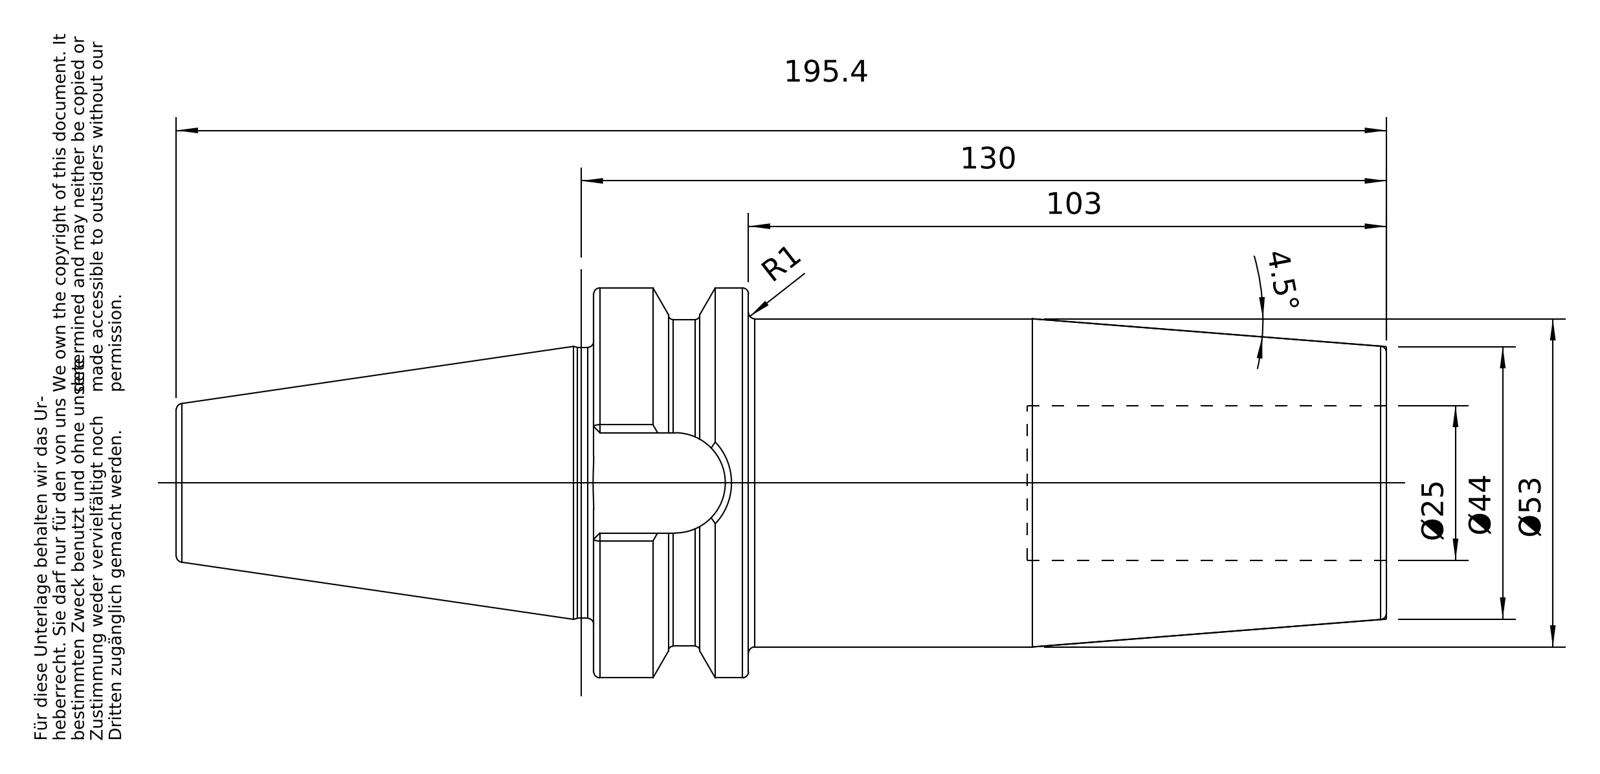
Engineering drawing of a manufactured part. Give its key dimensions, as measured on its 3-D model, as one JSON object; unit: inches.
{"part_name": "40-644-25", "step_written_by": "PRO/ENGINEER BY PARAMETRIC TECHNOLOGY CORPORATION, 2010430 (CONFIG_CONTROL_DESIGN)", "units": "inches", "bodies": {"solids": 1, "faces": 96, "planar": 26, "cylindrical": 22, "other": 48}, "overall_size": [7.693, 2.48, 2.48], "volume_in3": 18.59, "surface_area_in2": 65.02, "round_holes": [[0.545, 1], [0.67, 1], [0.689, 1], [0.984, 1]], "round_bosses_or_shafts": [[2.48, 1], [2.087, 1], [2.077, 1], [1.722, 1], [0.63, 1]], "partial_cylinders_radius": [[0.319, 1]], "face_to_face_distances": [5.039, 0.984, 4.055, 2.756, 1.772, 2.283, 1.768, 0.638, 2.654, 3.638]}
